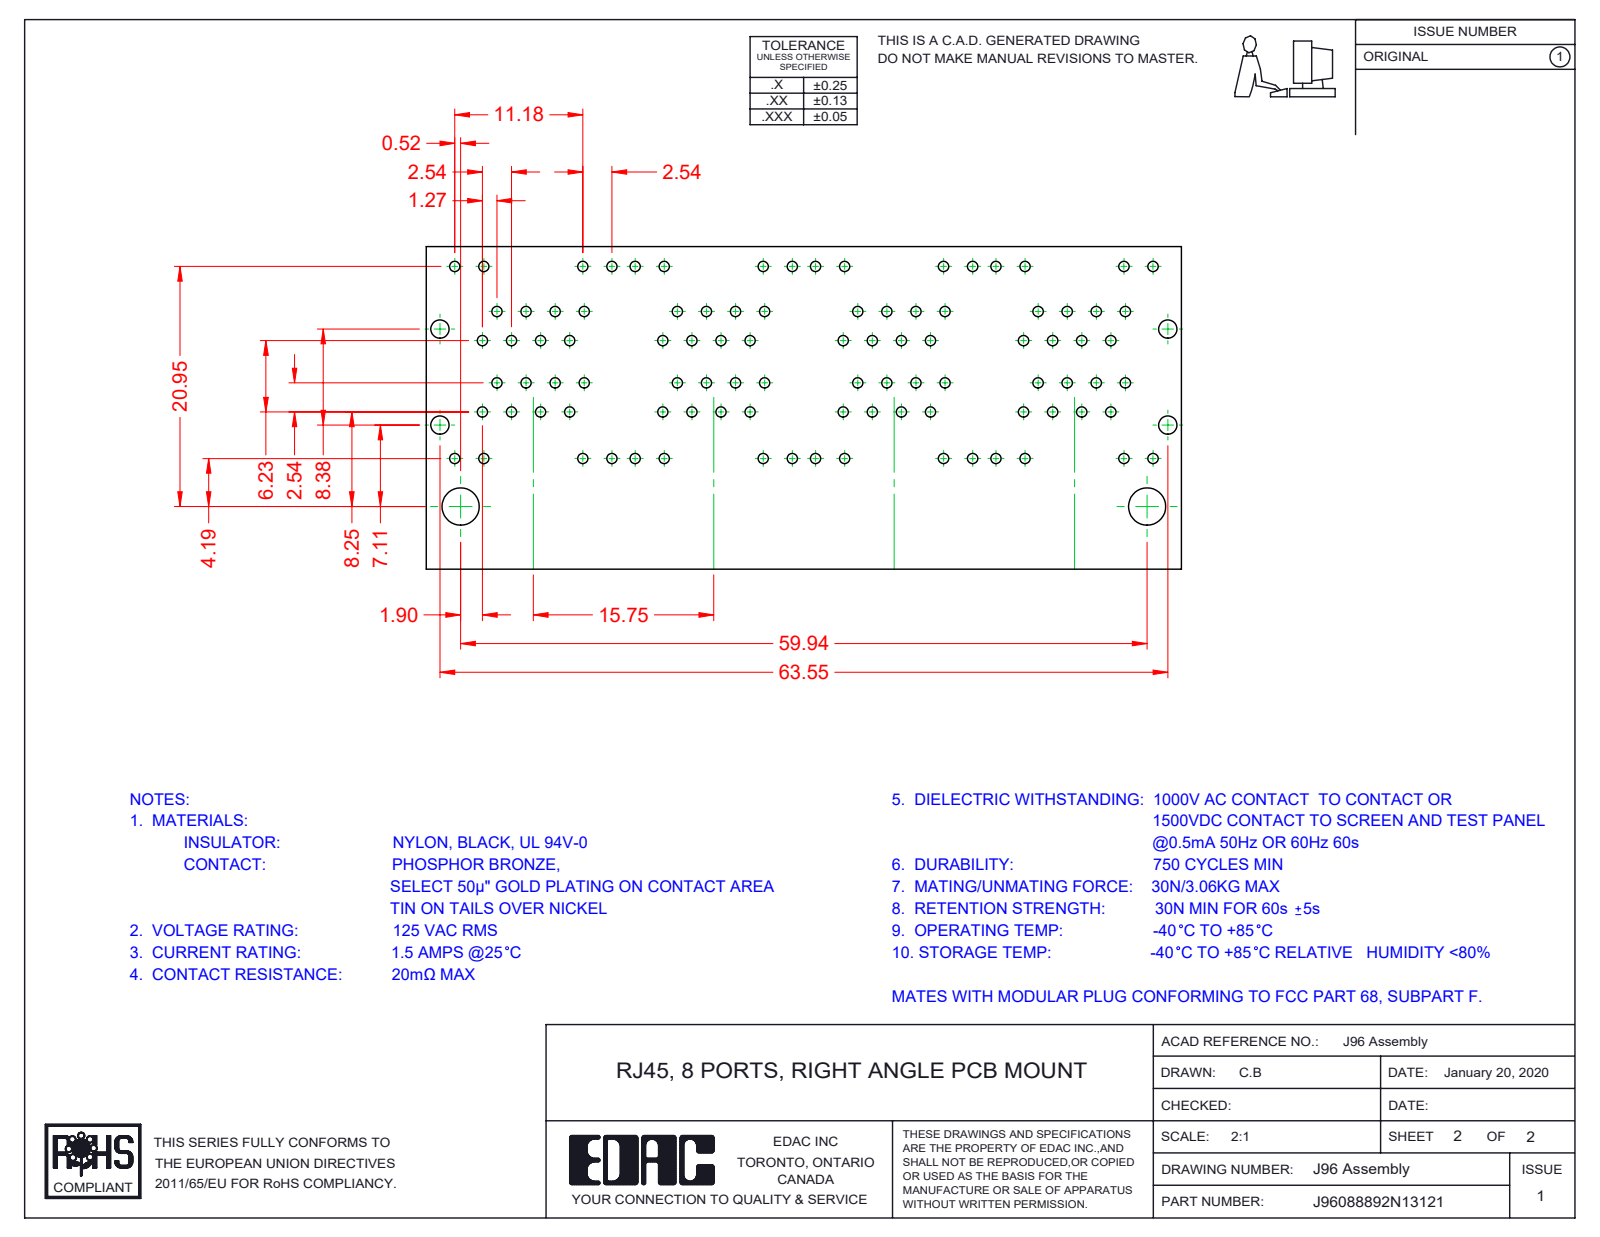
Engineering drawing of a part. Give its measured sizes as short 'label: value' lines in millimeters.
name: 96 LED RH Lower_3-Green; 96 Insulator Insert; 96 LED LH Lower_1-Yellow; 96 Contact Lock Upper (+8 more)
written by: SolidWorks 2016 (CONFIG_CONTROL_DESIGN)
unit: mm
bodies: 96 solids, 7642 faces (6069 planar, 1307 cylindrical, 266 other)
size: 64.05 × 29.58 × 28.68
volume: 24 160 mm³; area: 63 658 mm²
holes: 3× ⌀1.7
bosses: 3× ⌀1.68
rounds: 124× R0.25, 73× R0.35, 72× R1, 49× R0.5, 32× R0.91, 21× R0.2, 11× R0.7, 8× R0.22
face distances: 15.75, 0.35, 9.95, 1.17, 1.6, 0.54, 9.98, 10.18, 12.67, 3.37
hole spacings: 15.75, 31.5
